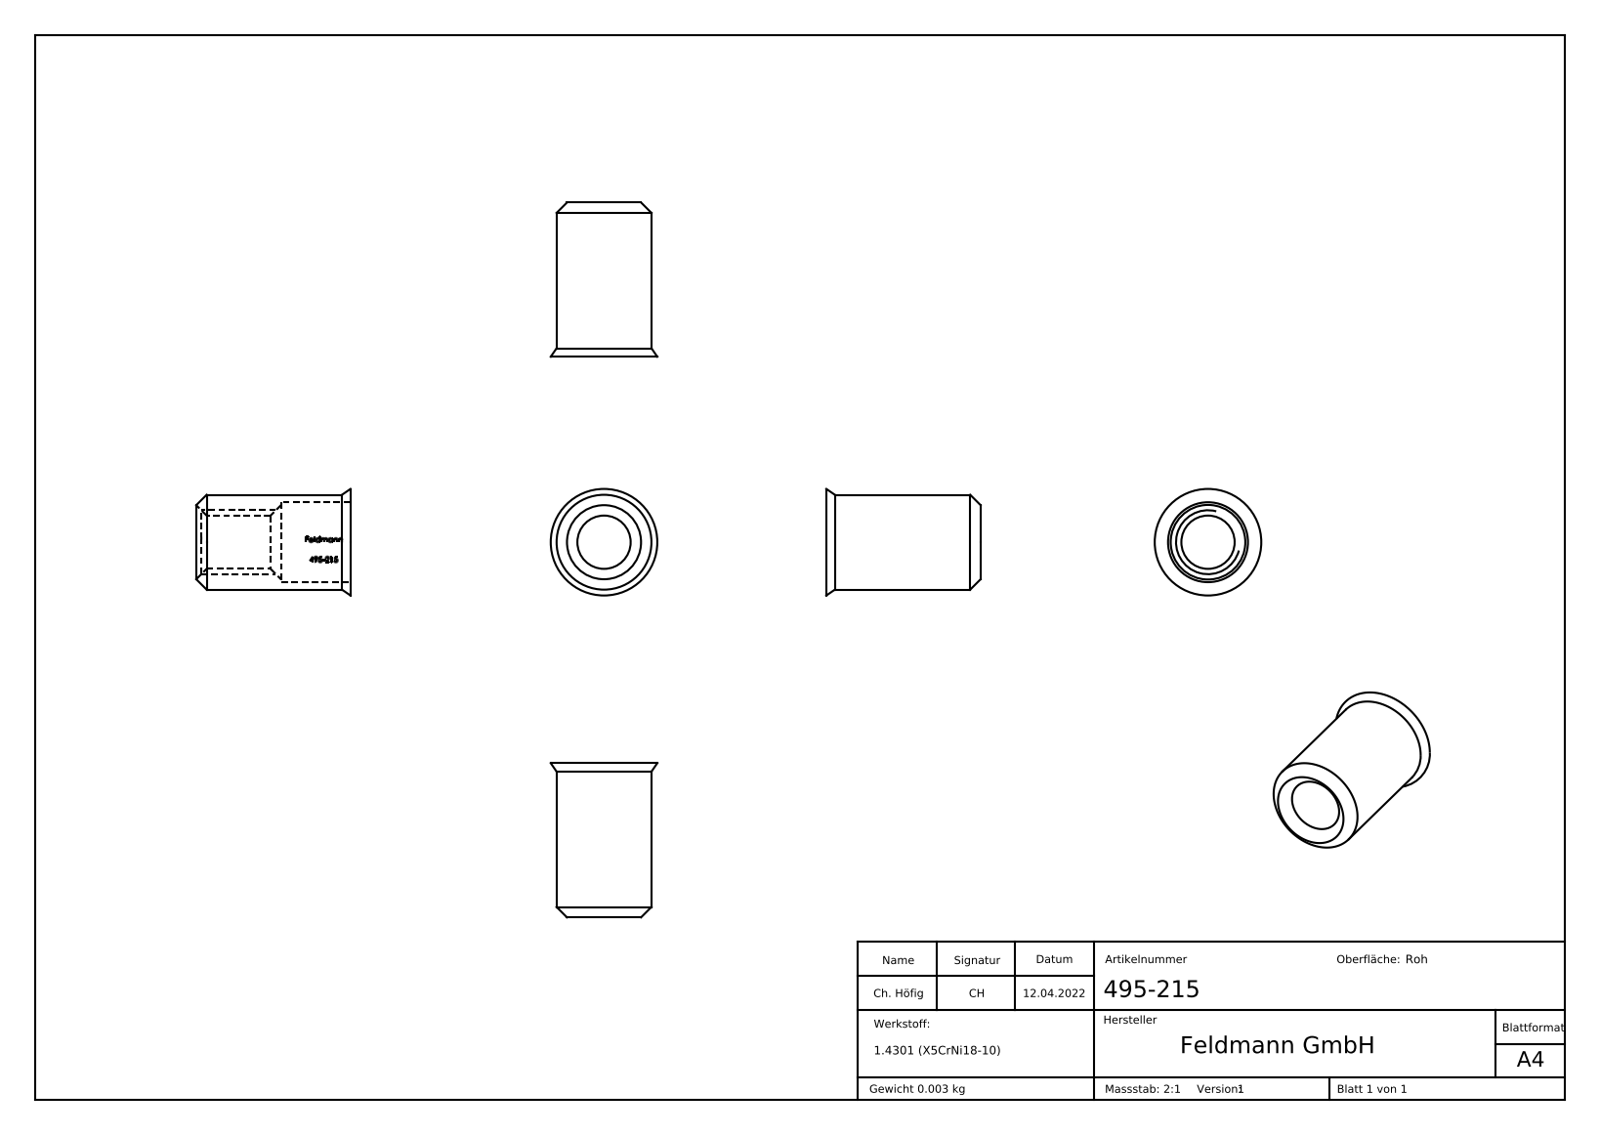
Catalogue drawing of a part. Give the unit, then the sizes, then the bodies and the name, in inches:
Units: inches
Overall size (bounding box): 0.57 × 0.394 × 0.394
Round holes (diameter × count): ⌀0.197 ×1, ⌀0.295 ×1
Round bosses / shafts (diameter × count): ⌀0.35 ×1
Partial cylindrical surfaces — rounded edges, fillets, slot ends (radius × count): R0.152 ×1
Main face-to-face distances: 0.256, 0.072, 0.026, 0.053, 0.074, 0.047, 0.069, 0.066, 0.064, 0.09
Volume: 0.026 in³ · Surface area: 1.18 in²
Bodies: 1 solid, 210 faces (100 planar, 29 cylindrical, 81 other)
Part name (STEP PRODUCT): 495-215
STEP written by: SolidWorks 2018 (CONFIG_CONTROL_DESIGN)
